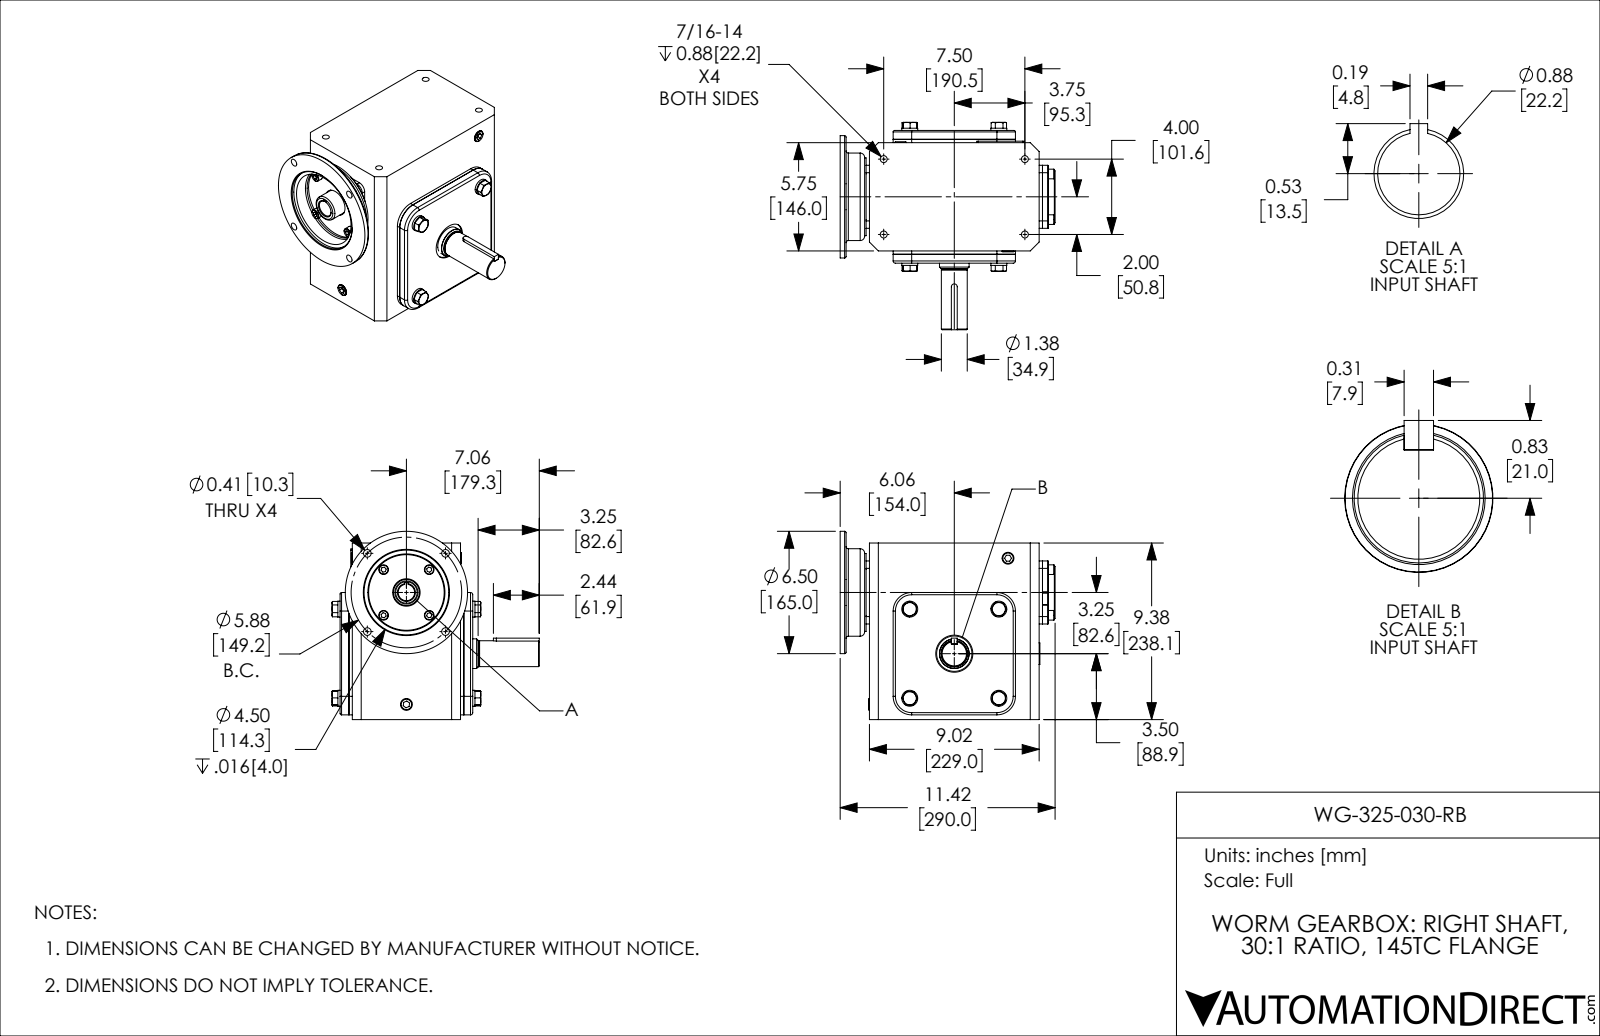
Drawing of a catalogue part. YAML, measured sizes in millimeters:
part_name: "WG-325-030-RB"
step_written_by: "SolidWorks 2017 (AUTOMOTIVE_DESIGN)"
units: millimeters
bodies: {solids: 39, faces: 576, planar: 318, cylindrical: 168, other: 90}
overall_size: [290, 279.8, 253.9]
volume: 8259000
surface_area: 582200
round_holes:
  - {diameter: 9.3, count: 4}
  - {diameter: 10.3, count: 4}
  - {diameter: 16, count: 3}
  - {diameter: 15, count: 1}
  - {diameter: 22.2, count: 1}
  - {diameter: 24.8, count: 1}
  - {diameter: 30, count: 1}
  - {diameter: 37, count: 1}
  - {diameter: 50, count: 1}
  - {diameter: 62, count: 1}
  - {diameter: 70, count: 1}
  - {diameter: 102, count: 1}
round_bosses_or_shafts:
  - {diameter: 21.5, count: 4}
  - {diameter: 13, count: 4}
  - {diameter: 165, count: 1}
  - {diameter: 118, count: 1}
  - {diameter: 105, count: 1}
  - {diameter: 72, count: 1}
  - {diameter: 40, count: 1}
  - {diameter: 35, count: 1}
partial_cylinders:
  - {radius: 2, count: 11}
  - {radius: 3, count: 4}
  - {radius: 10, count: 4}
  - {radius: 23, count: 4}
  - {radius: 25, count: 4}
  - {radius: 0.5, count: 2}
  - {radius: 1, count: 2}
  - {radius: 4, count: 1}
face_to_face_distances: [2, 4.5, 165, 10, 177, 12, 167, 162.5, 14.5, 16.5]
hole_center_spacings: [74.6, 105.5, 60.6, 101.6, 111.5, 145.2, 147.8, 149.2]
